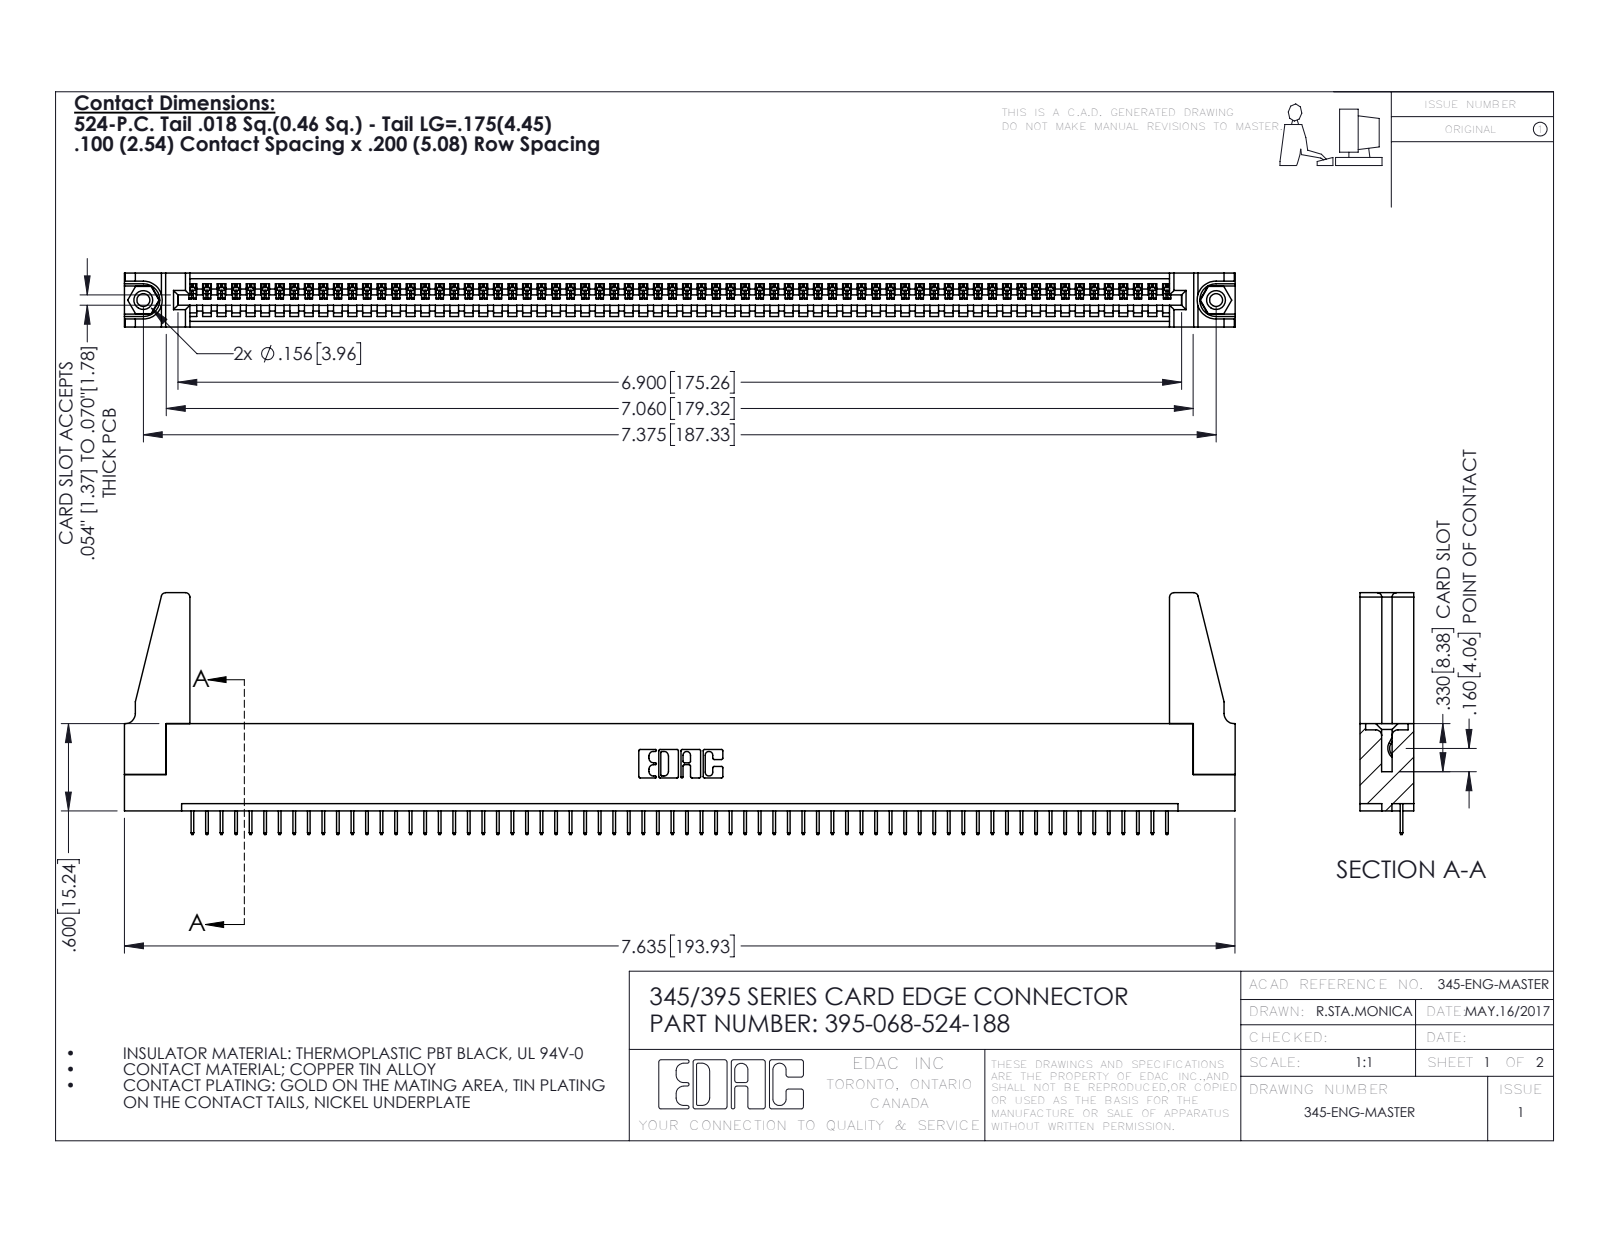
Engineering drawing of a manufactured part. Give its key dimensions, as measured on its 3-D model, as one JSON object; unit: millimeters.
{"part_name": "345 Part_Flush Mounting Lugs - 0.156 Dia-TH; 395-068-524-188; 345-292-001_345-293-124; 345-220-078_345-220-088 (+1 more)", "step_written_by": "SolidWorks 2016 (CONFIG_CONTROL_DESIGN)", "units": "millimeters", "bodies": {"solids": 73, "faces": 4466, "planar": 3280, "cylindrical": 1170, "other": 16}, "overall_size": [194, 42.2, 9.4], "volume_mm3": 21610, "surface_area_mm2": 27030, "round_holes": [[2.3, 2], [3.2, 2], [4, 2], [1.6, 1]], "round_bosses_or_shafts": [[3.9, 2]], "partial_cylinders_radius": [[0.2, 136], [0.3, 22], [0.8, 8], [0.2, 6], [0.8, 6], [0.7, 3], [0.8, 2], [1, 2]], "face_to_face_distances": [1.8, 7.6, 9.4, 5.1, 2.5, 6.9, 0.6, 5.7, 1.8, 3.8], "hole_center_spacings": [6.9, 181.3, 187.3]}
